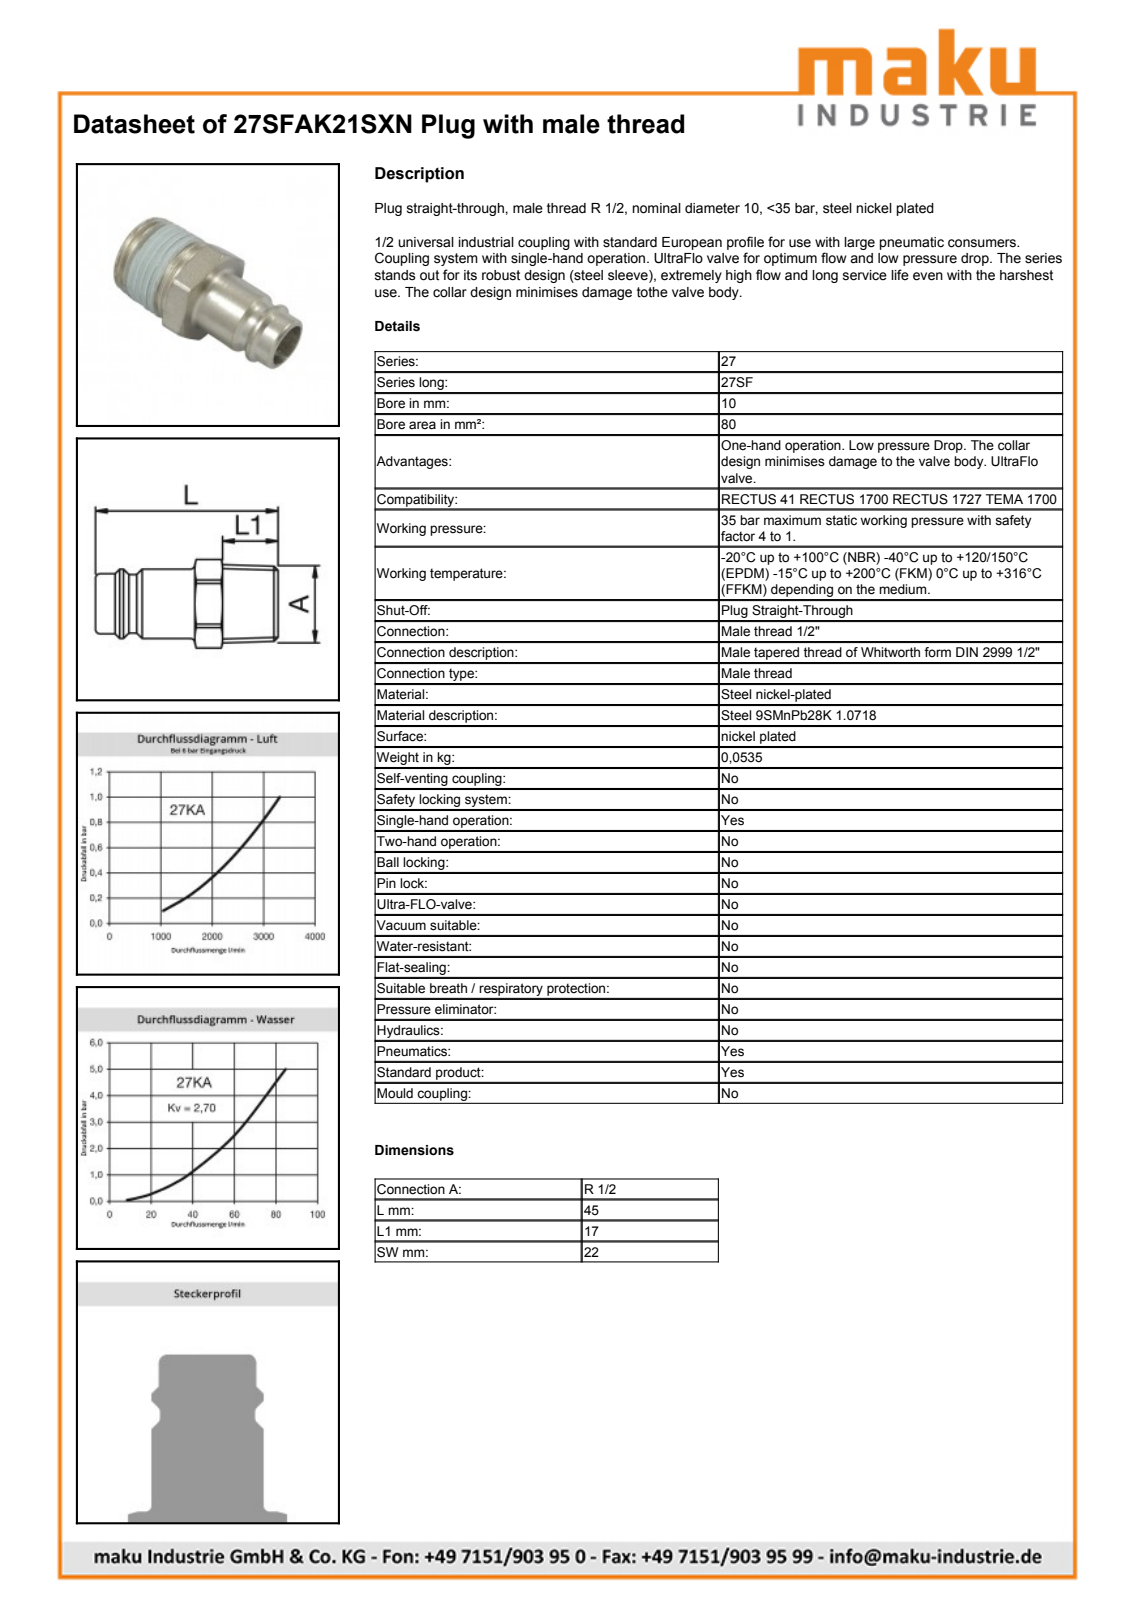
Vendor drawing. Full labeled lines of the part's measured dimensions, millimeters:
Part name (STEP PRODUCT): D106713
STEP written by: Autodesk Inventor 2011 (AUTOMOTIVE_DESIGN)
Units: millimetres
Bodies: 1 solid, 44 faces (10 planar, 12 cylindrical, 22 other)
Overall size (bounding box): 45 × 24.8 × 22
Volume: 7 578 mm³ · Surface area: 4 681 mm²
Round holes (diameter × count): ⌀10 ×1, ⌀12.6 ×1
Round bosses / shafts (diameter × count): ⌀15 ×1, ⌀13 ×1, ⌀12.65 ×1
Partial cylindrical surfaces — rounded edges, fillets, slot ends (radius × count): R12.4 ×1
Main face-to-face distances: 22, 23.5, 21.5, 45, 28, 6.5, 17
